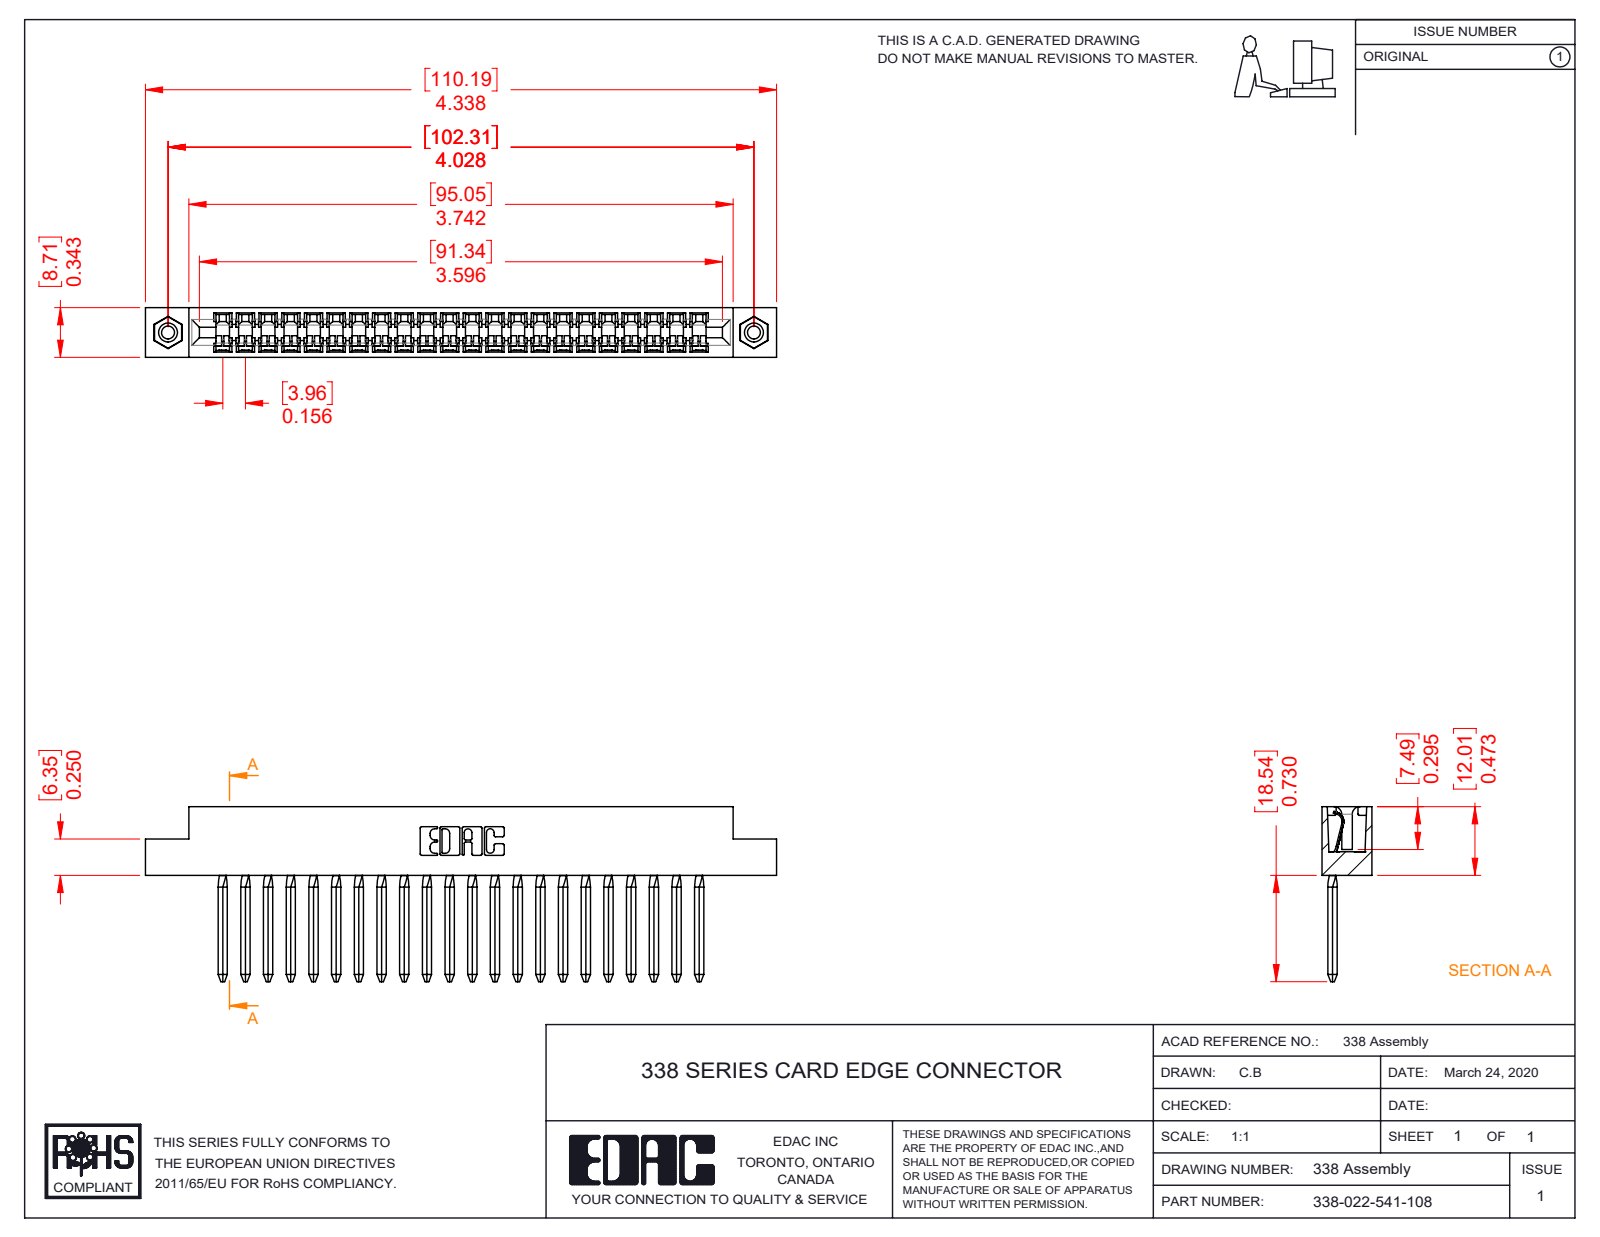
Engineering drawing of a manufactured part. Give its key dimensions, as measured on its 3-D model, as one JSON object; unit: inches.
{"part_name": "338-210-001_338-210-022-004; 345-250-001_345-250-003-102; 338-290-001_541; 338-022-541-108", "step_written_by": "SolidWorks 2016 (CONFIG_CONTROL_DESIGN)", "units": "inches", "bodies": {"solids": 25, "faces": 2200, "planar": 1512, "cylindrical": 584, "other": 104}, "overall_size": [4.338, 1.203, 0.343], "volume_in3": 0.47, "surface_area_in2": 19.27, "round_holes": [[0.089, 2], [0.125, 2], [0.156, 2]], "round_bosses_or_shafts": [[0.155, 2]], "partial_cylinders_radius": [[0.025, 90], [0.008, 22], [0.01, 22], [0.055, 18], [0.067, 18], [0.1, 17], [0.007, 6], [0.031, 6]], "face_to_face_distances": [0.343, 0.156, 0.11, 0.624, 0.207, 0.135, 0.78, 0.468, 0.221, 0.312], "hole_center_spacings": [4.028]}
